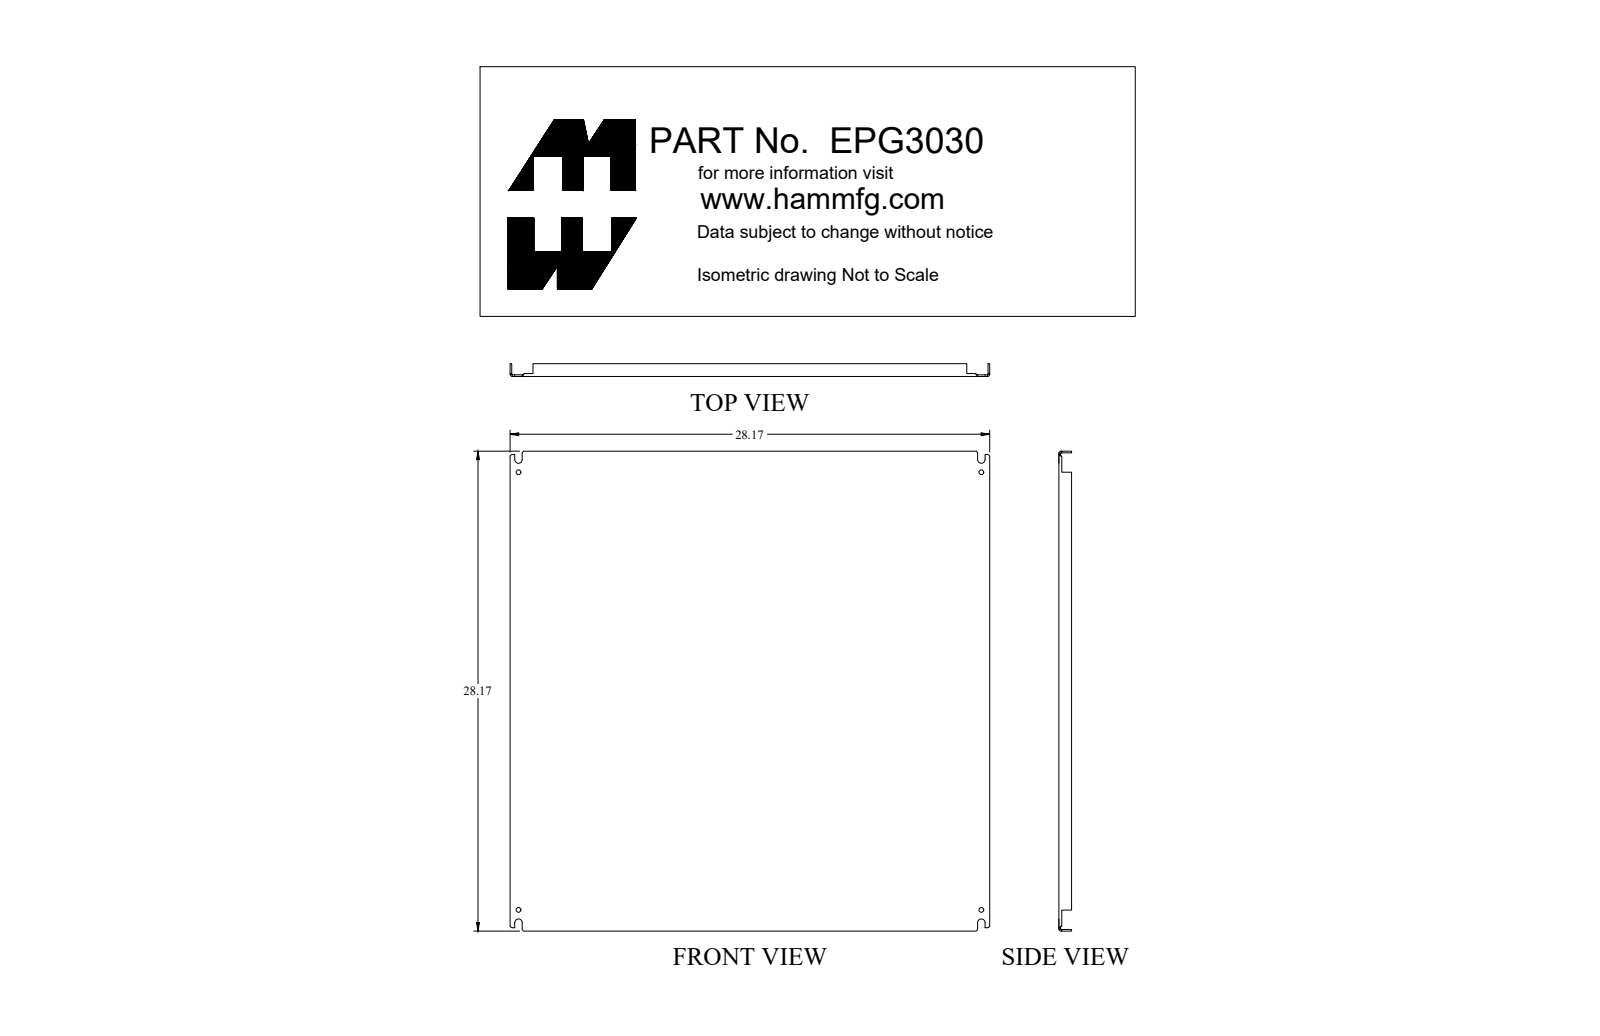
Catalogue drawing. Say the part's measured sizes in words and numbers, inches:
The part is named "EPG3030". Its 3-D file was written by "SolidWorks 2018 (AUTOMOTIVE_DESIGN)". It is 1 solid with 128 faces: 74 planar, 38 cylindrical and 16 other. Overall it measures 28.17 by 28.17 by 0.75 inches. Its volume is 81.21 cubic inches and its surface area 1 721 square inches. Round holes: 4 of diameter 0.281. Partial cylindrical surfaces (rounded edges, fillets, slot ends): 4 of radius 0.048, 4 of radius 0.063, 4 of radius 0.143, 4 of radius 0.219. The main face-to-face distances are 0.095, 28.075, 27.98, 28.17, 0.75, 0.655, 0.171, 0.076, 0.579, 1.235. The hole center spacings are 25.688, 27.188, 37.404.
